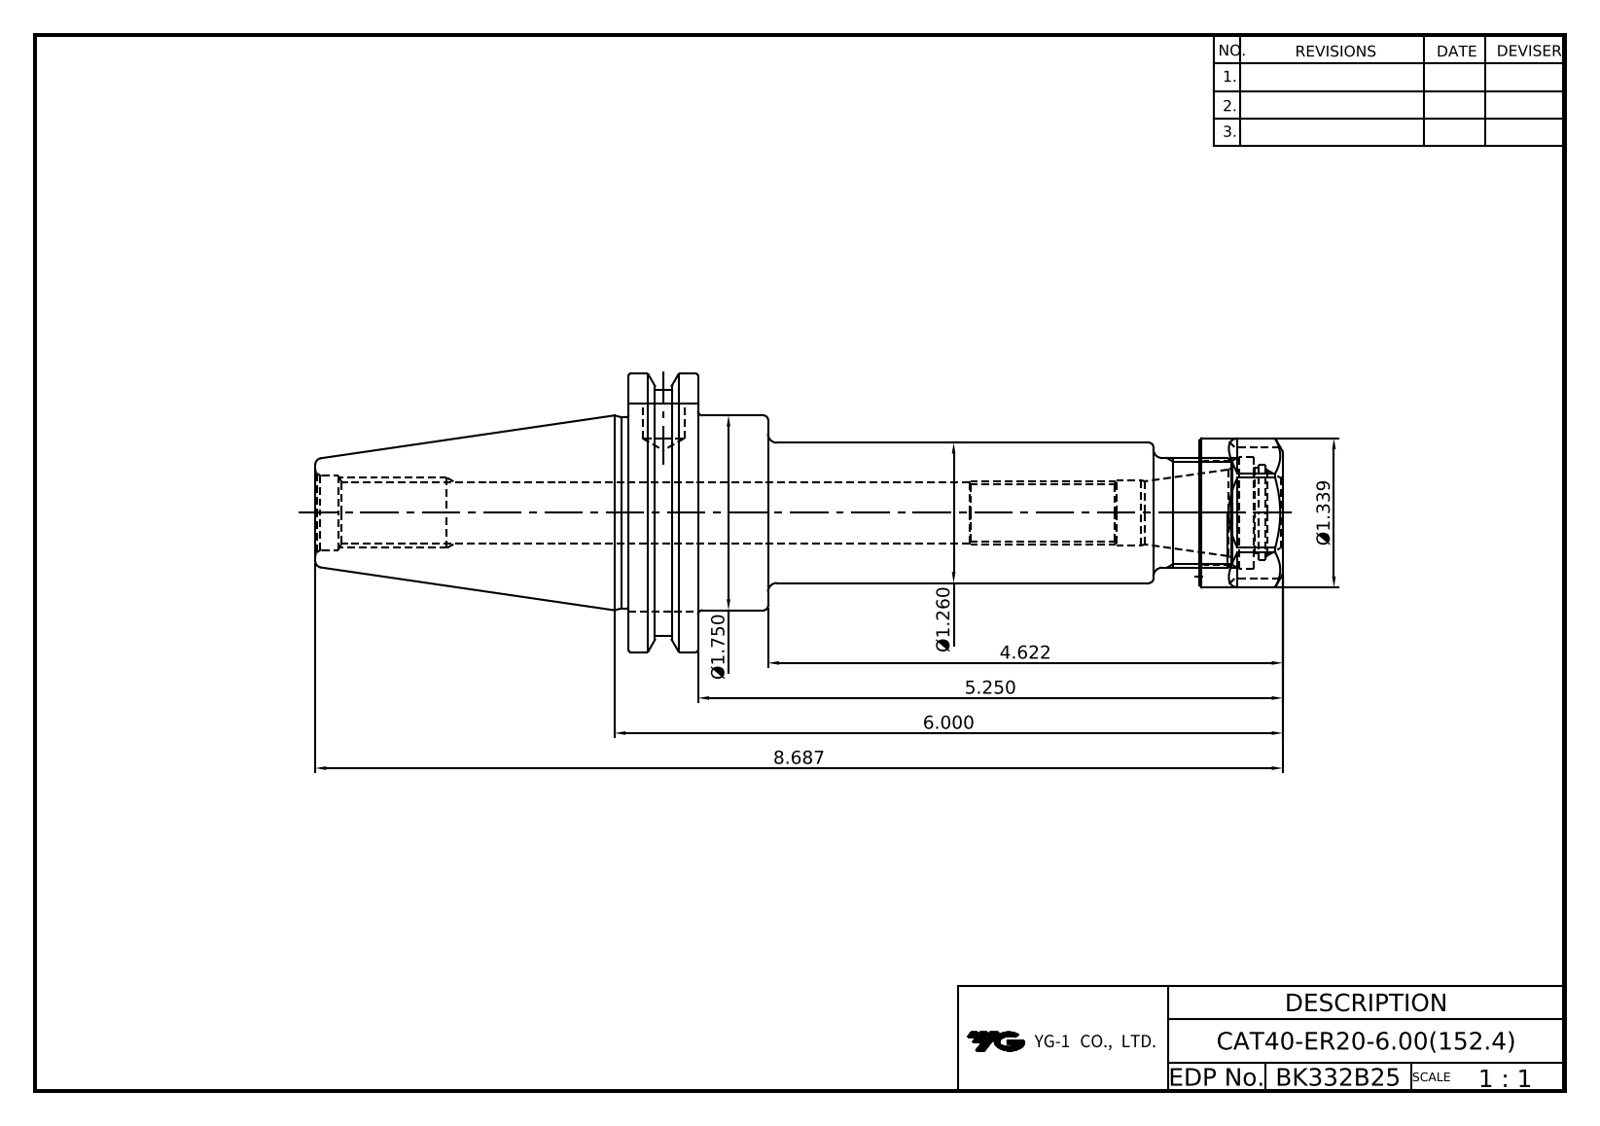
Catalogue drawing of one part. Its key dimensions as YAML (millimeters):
part_name: "LO-CAT40-ER20-152.4; ER20NUT"
step_written_by: "Autodesk Inventor 2025 (AUTOMOTIVE_DESIGN)"
units: millimeters
bodies: {solids: 2, faces: 92, planar: 49, cylindrical: 22, other: 21}
overall_size: [220.65, 63.5, 61.09]
volume: 195468
surface_area: 43136
round_holes:
  - {diameter: 9.53, count: 1}
  - {diameter: 12.57, count: 1}
  - {diameter: 13.39, count: 1}
  - {diameter: 14.9, count: 1}
  - {diameter: 16, count: 1}
  - {diameter: 16.3, count: 1}
  - {diameter: 18.4, count: 1}
  - {diameter: 21.76, count: 1}
  - {diameter: 23.5, count: 1}
  - {diameter: 25.5, count: 1}
round_bosses_or_shafts:
  - {diameter: 63.5, count: 1}
  - {diameter: 56.3, count: 1}
  - {diameter: 44.45, count: 1}
  - {diameter: 43.6, count: 1}
  - {diameter: 34, count: 1}
  - {diameter: 32, count: 1}
  - {diameter: 25, count: 1}
face_to_face_distances: [15.88, 31.83, 15.95, 149.23, 133.35, 117.4, 19, 130.23, 114.35, 98.4]
